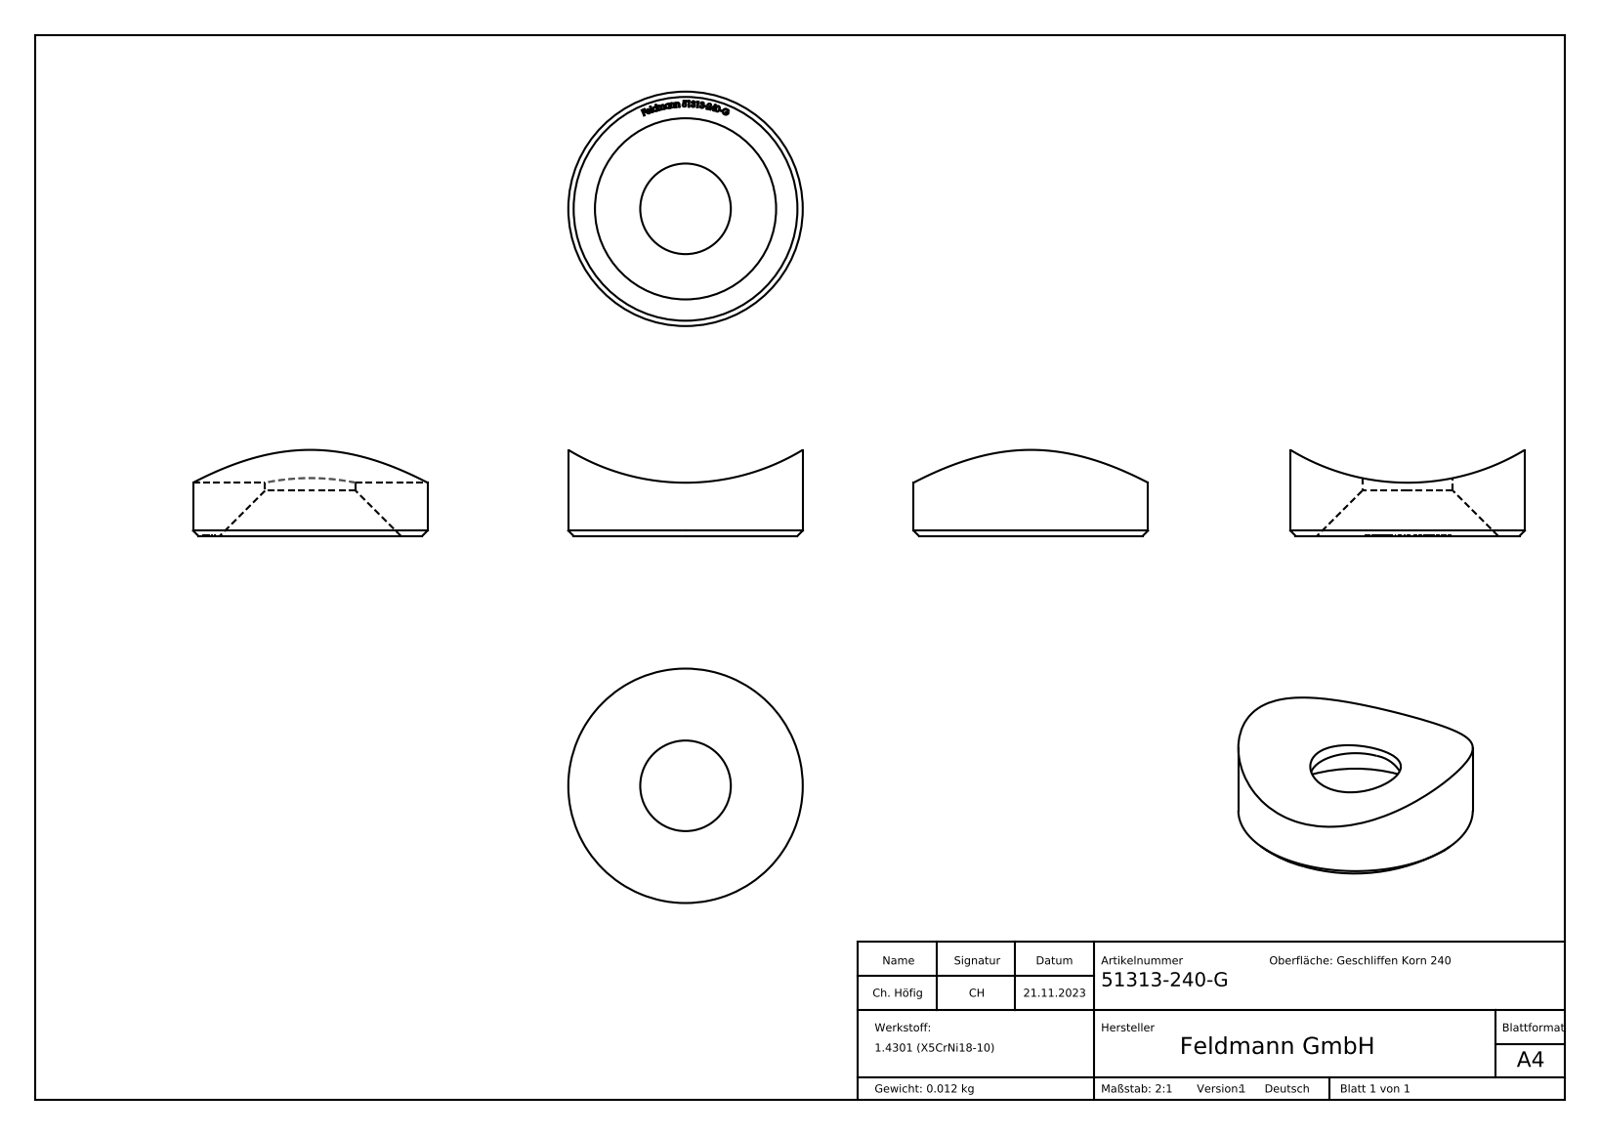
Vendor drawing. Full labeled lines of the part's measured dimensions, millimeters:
Part name (STEP PRODUCT): 51313-240-G
STEP written by: SolidWorks 2018 (CONFIG_CONTROL_DESIGN)
Units: millimetres
Bodies: 1 solid, 247 faces (134 planar, 3 cylindrical, 110 other)
Overall size (bounding box): 22 × 22 × 8.08
Volume: 1 562 mm³ · Surface area: 1 191 mm²
Round holes (diameter × count): ⌀8.5 ×1
Round bosses / shafts (diameter × count): ⌀22 ×1
Partial cylindrical surfaces — rounded edges, fillets, slot ends (radius × count): R21.2 ×1
Main face-to-face distances: 0.53, 0.58, 0.48, 0.39, 0.34, 0.52, 0.36, 0.54, 0.38, 0.37
